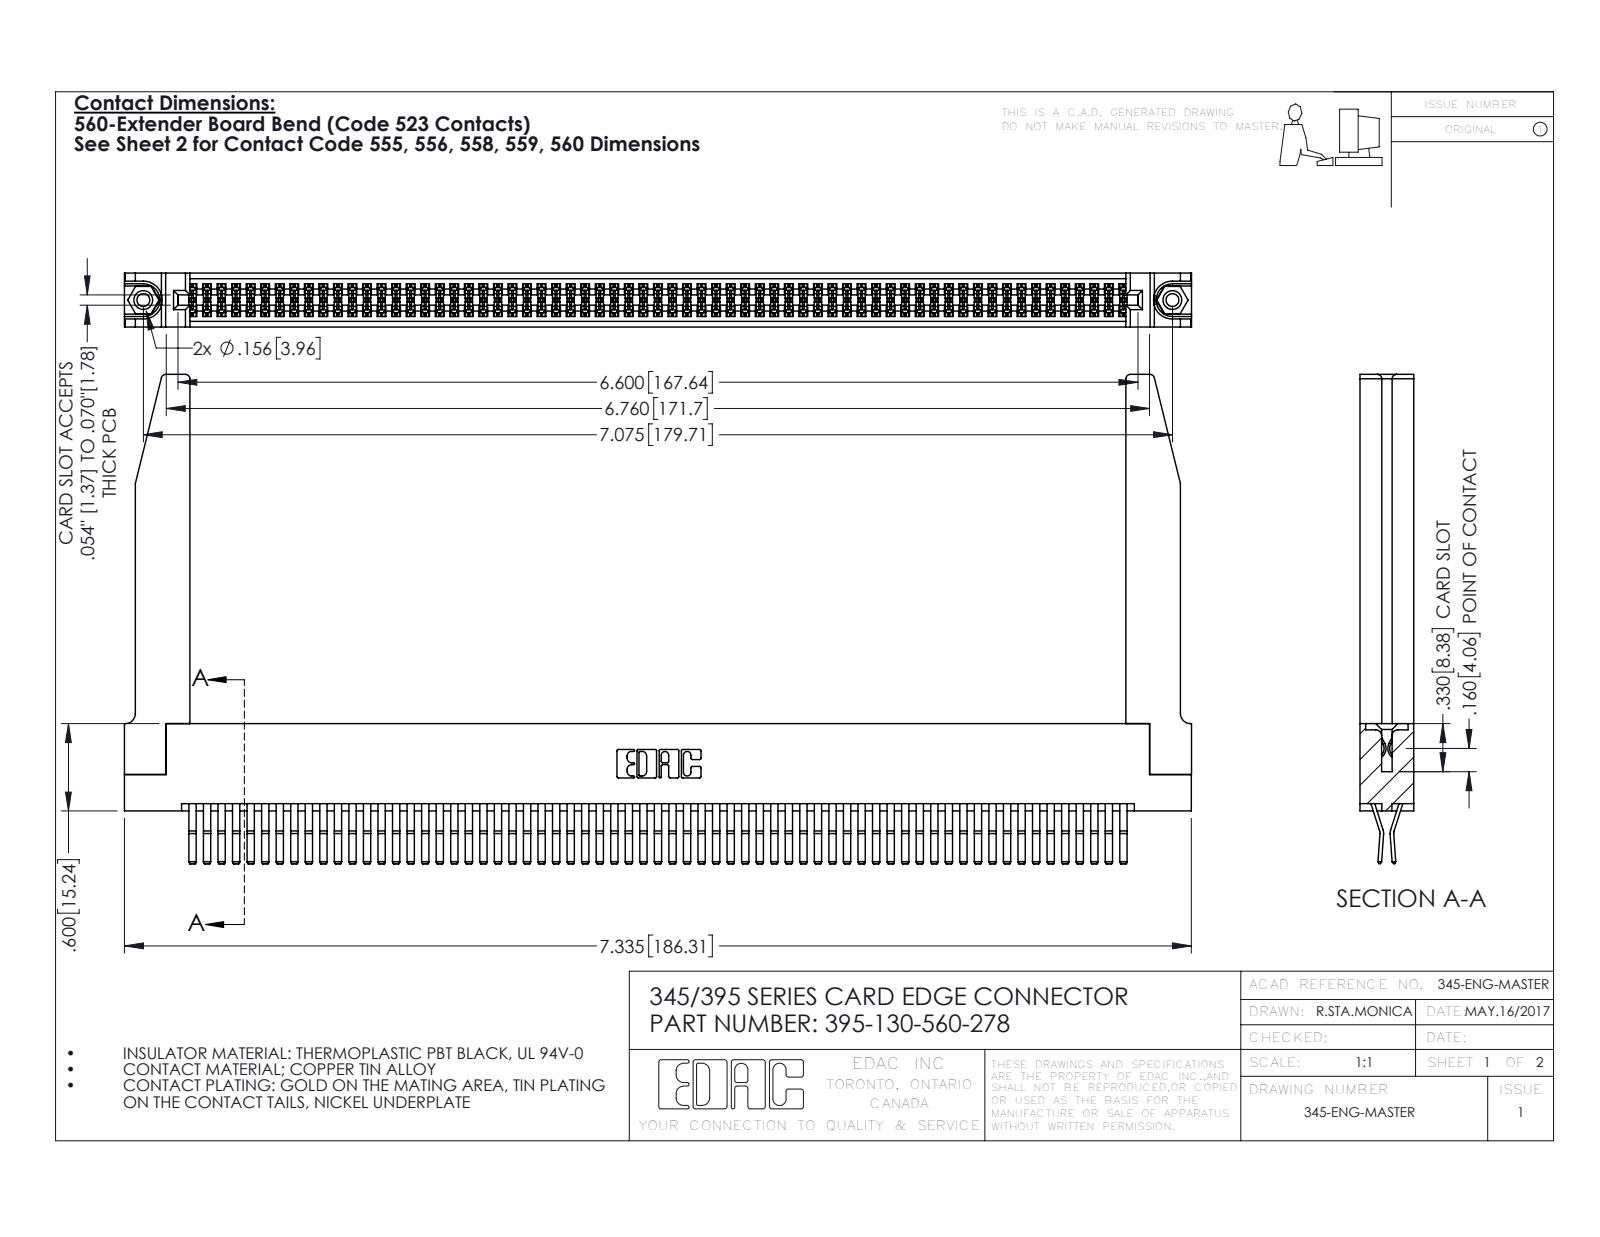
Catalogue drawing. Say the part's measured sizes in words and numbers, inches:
The part is named "345-250-001_345-250-001-102; 345-292-001_560 Tail; 345-220-078_345-220-078; 395-130-560-278 (+1 more)". Its 3-D file was written by "SolidWorks 2016 (CONFIG_CONTROL_DESIGN)". It is 135 solids with 7120 faces: 4512 planar, 2556 cylindrical and 52 other. Overall it measures 7.336 by 3.362 by 0.37 inches. Its volume is 1.644 cubic inches and its surface area 58.6 square inches. Round holes: 2 of diameter 0.089, 2 of diameter 0.125, 2 of diameter 0.156, 1 of diameter 0.064. Round bosses or shafts: 2 of diameter 0.155. Partial cylindrical surfaces (rounded edges, fillets, slot ends): 195 of radius 0.006, 22 of radius 0.01, 8 of radius 0.03, 6 of radius 0.007, 6 of radius 0.031, 3 of radius 0.026, 2 of radius 0.01, 2 of radius 0.014. The main face-to-face distances are 0.072, 0.298, 0.025, 0.37, 0.2, 0.098, 0.272, 0.225, 0.175, 0.148. The hole center spacings are 0.27, 6.839, 7.075.
